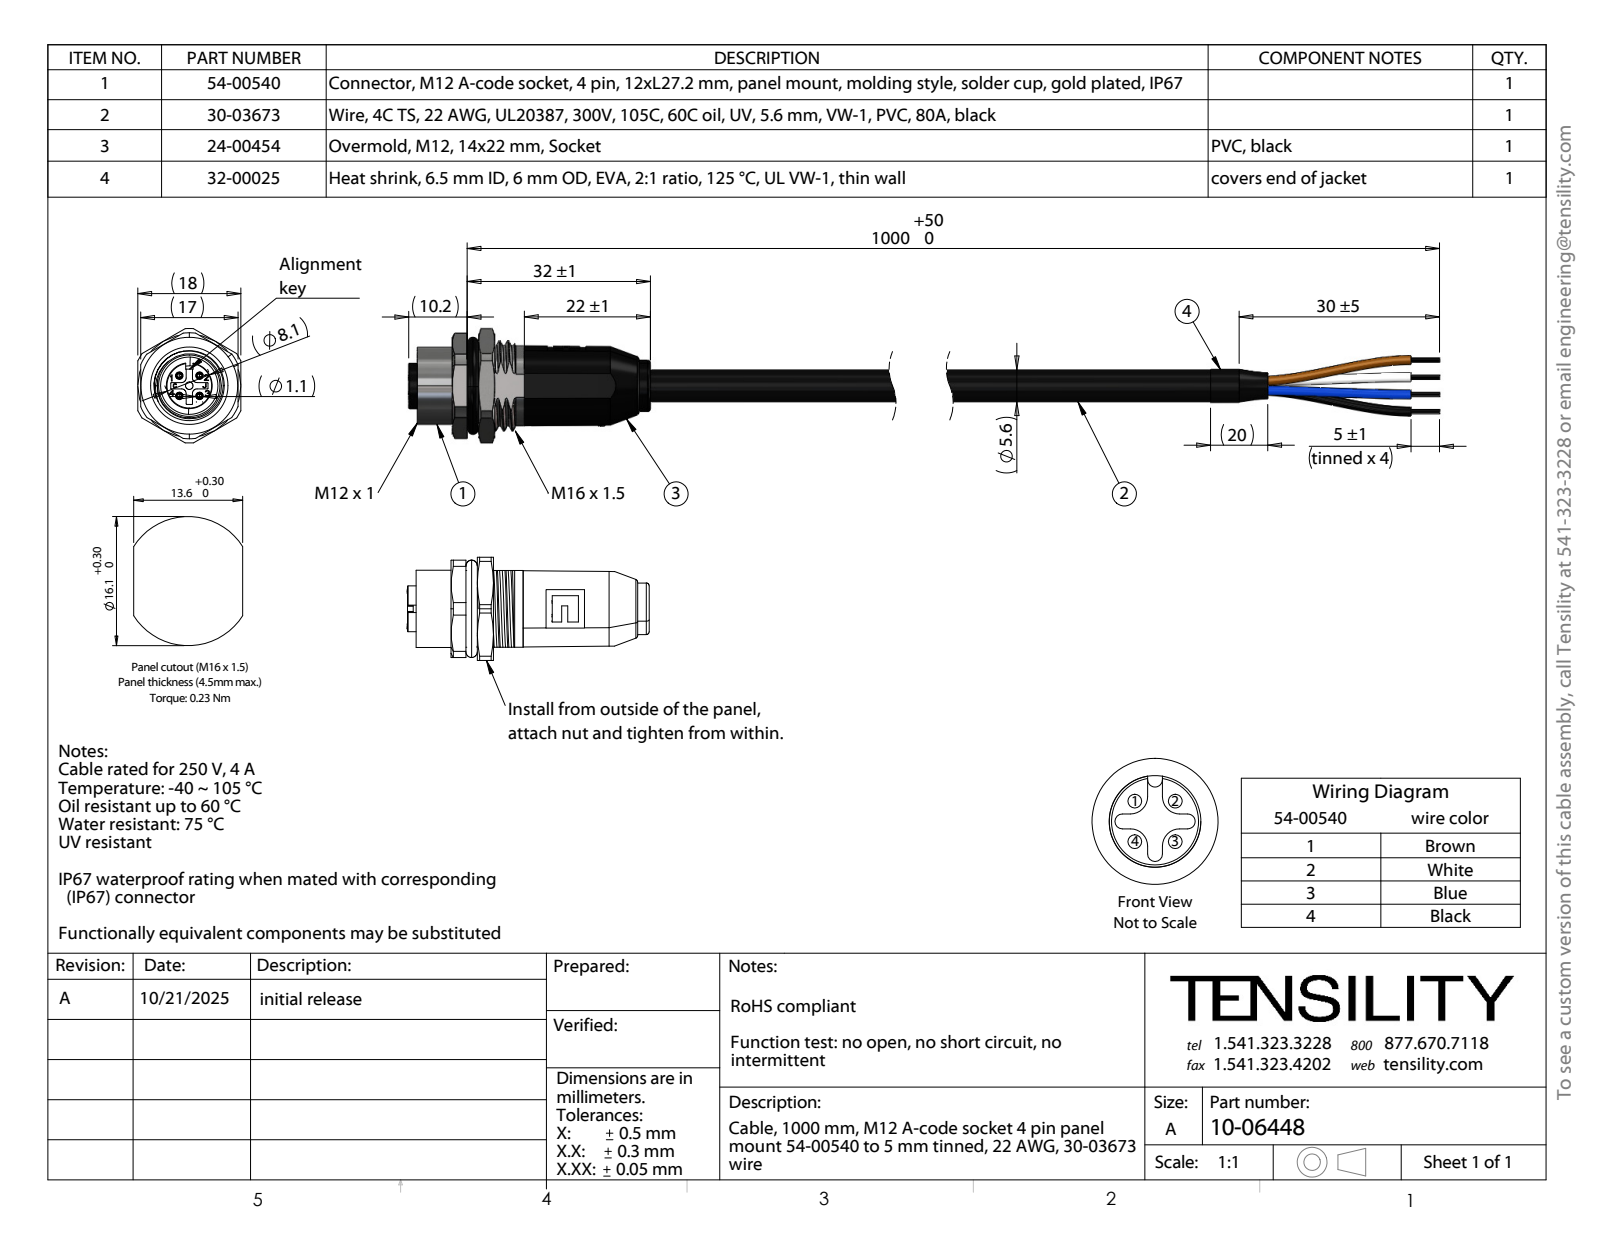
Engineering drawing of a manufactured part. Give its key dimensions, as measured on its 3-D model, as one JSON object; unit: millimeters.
{"part_name": "54-00540; 24-00454; 56-00046; 30-03673_spec (+2 more)", "step_written_by": "SolidWorks 2025 (CONFIG_CONTROL_DESIGN)", "units": "millimeters", "bodies": {"solids": 155, "faces": 1614, "planar": 715, "cylindrical": 659, "other": 240}, "overall_size": [227.24, 20, 18], "volume_mm3": 9951, "surface_area_mm2": 34725, "round_holes": [[1.6, 8], [1.3, 5], [1.2, 4], [3.88, 1], [4.28, 1], [6.5, 1], [7.5, 1], [8.8, 1], [9.1, 1], [9.6, 1], [11.2, 1], [12.2, 1]], "round_bosses_or_shafts": [[1.7, 4], [1.56, 4], [1.52, 4], [13.95, 1], [13.5, 1], [12.5, 1], [11, 1], [10.7, 1]], "partial_cylinders_radius": [[0.1, 6], [0.8, 4], [0.5, 3], [7.04, 1], [7.9, 1], [9.25, 1], [10, 1]], "face_to_face_distances": [0.5, 10, 2, 9.5, 11.5, 18, 7.5, 2.6, 1.5, 5.1], "hole_center_spacings": [0.48, 0.37, 1.62, 0.31, 0.33, 1.78, 0.32, 1.45]}
